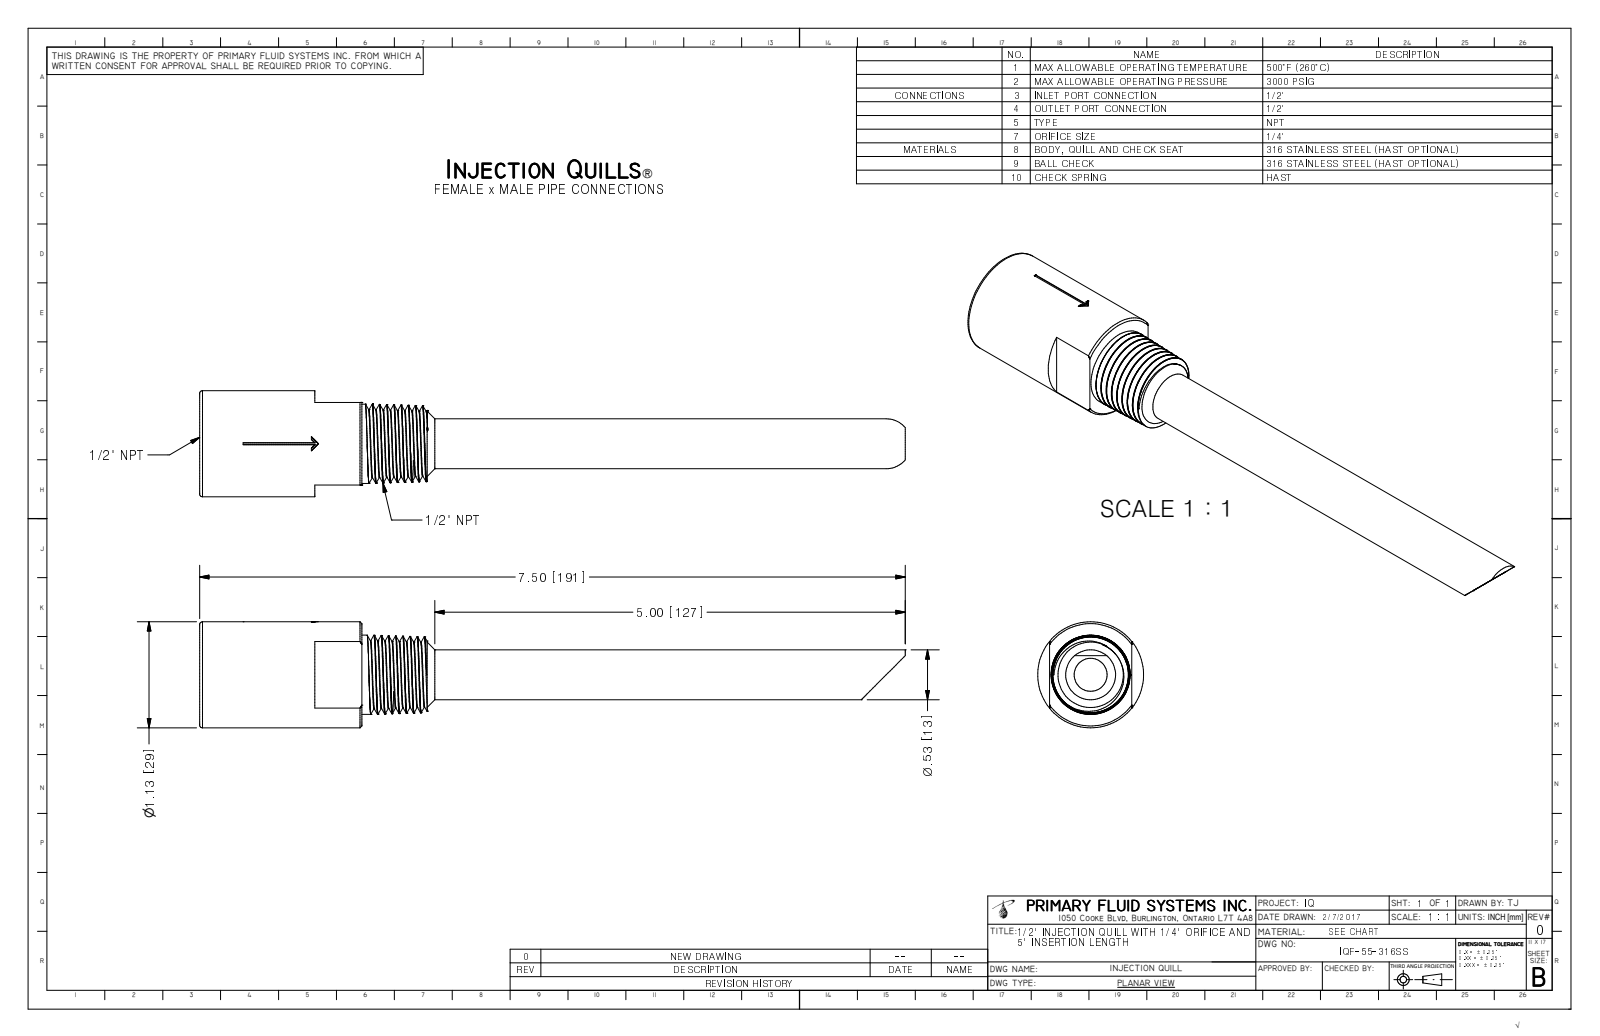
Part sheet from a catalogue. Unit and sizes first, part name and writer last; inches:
Units: inches
Overall size (bounding box): 7.5 × 1.125 × 1.125
Round holes (diameter × count): ⌀0.35 ×1, ⌀0.438 ×1, ⌀0.703 ×1
Round bosses / shafts (diameter × count): ⌀1.125 ×1, ⌀0.84 ×1, ⌀0.53 ×1
Partial cylindrical surfaces — rounded edges, fillets, slot ends (radius × count): R0.558 ×1
Main face-to-face distances: 0.875, 1.725, 0.5, 0.475, 0.75, 1.225, 0.65, 0.975, 1.25, 0.1
Volume: 1.986 in³ · Surface area: 29.96 in²
Bodies: 1 solid, 68 faces (36 planar, 7 cylindrical, 25 other)
Part name (STEP PRODUCT): IQF-55-316SS_R0
STEP written by: Autodesk Inventor 2009 (AUTOMOTIVE_DESIGN)
